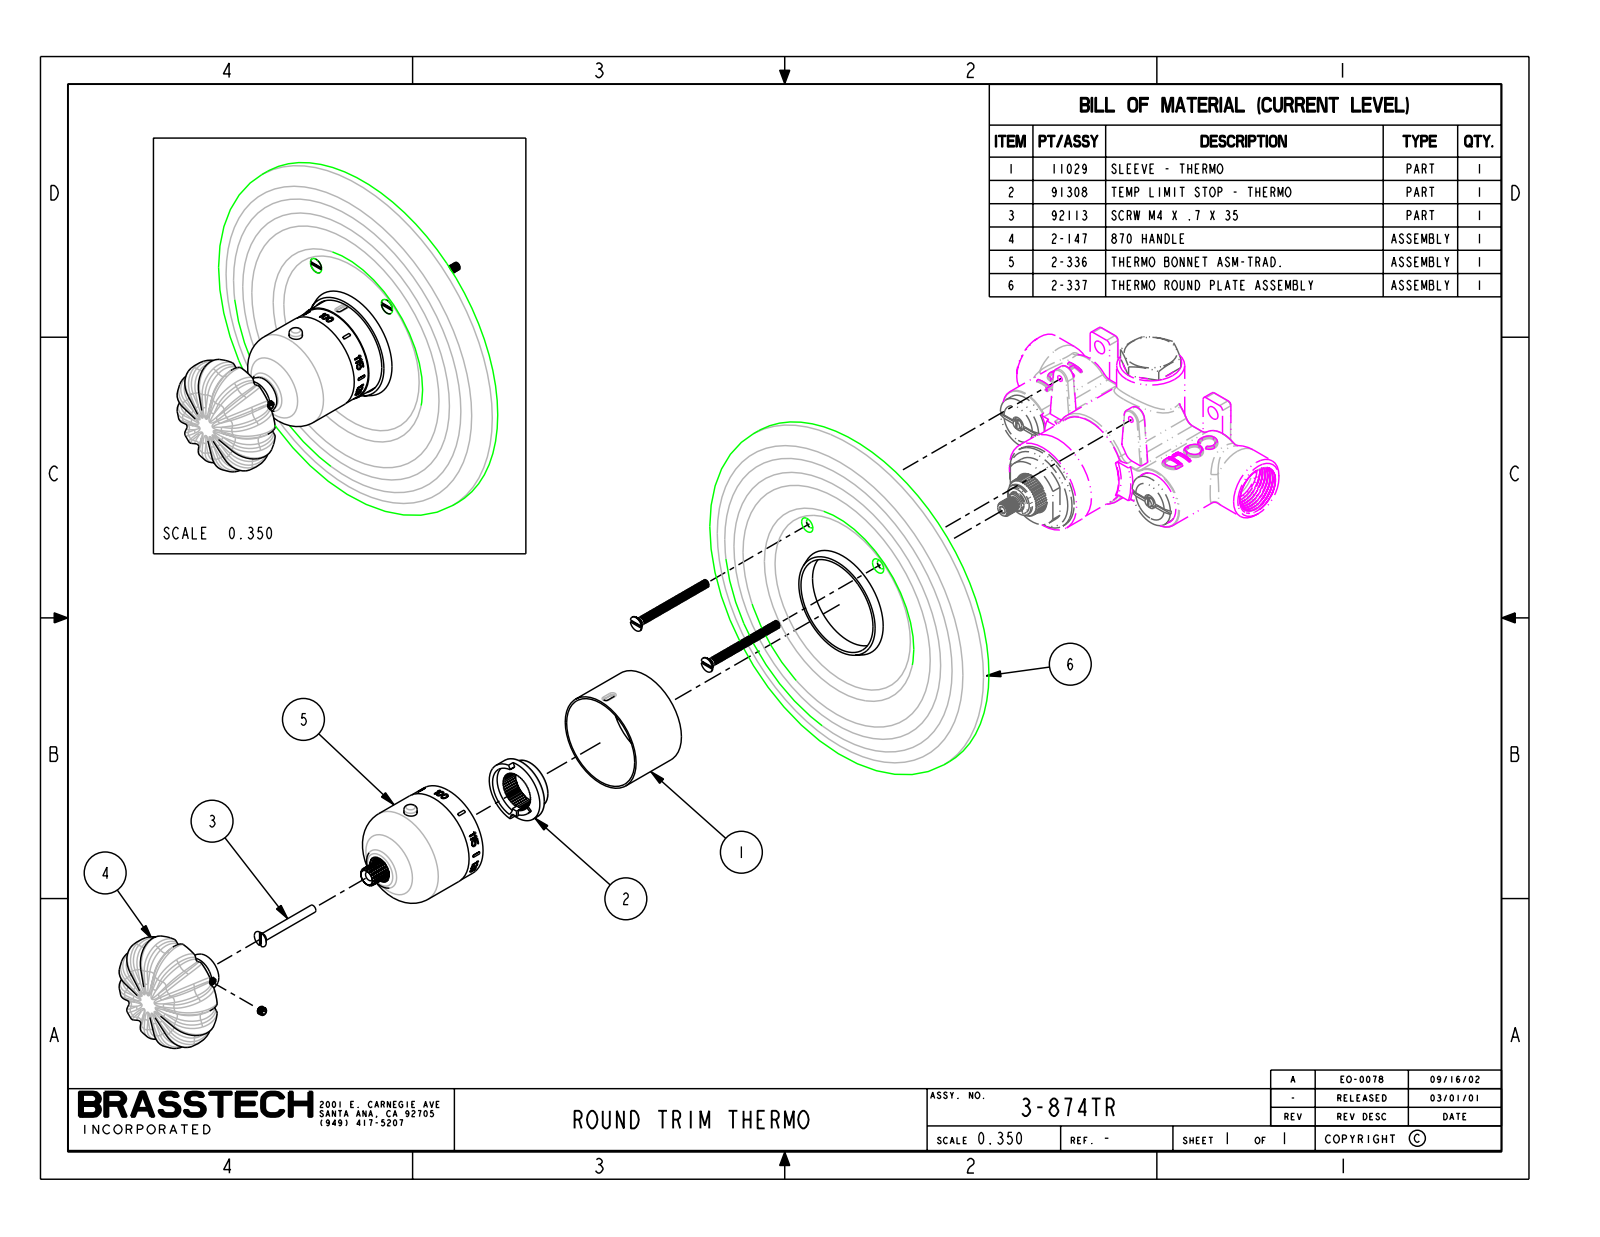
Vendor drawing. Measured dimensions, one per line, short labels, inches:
name: 3-874TR
written by: CREO PARAMETRIC BY PTC INC, 2018400 (CONFIG_CONTROL_DESIGN)
unit: in
bodies: 1 solid, 696 faces (329 planar, 33 cylindrical, 334 other)
size: 7.5 × 7.5 × 4.357
volume: 27.4 in³; area: 124.2 in²
bosses: 1× ⌀7.5, 1× ⌀1.97, 1× ⌀1.94, 1× ⌀1.929, 1× ⌀0.37, 1× ⌀0.26, 1× ⌀0.067
rounds: 1× R0.969
face distances: 0.313, 3.487, 3.174, 0.159, 0.471, 3.016, 0.031, 2.706, 2.394, 2.235
